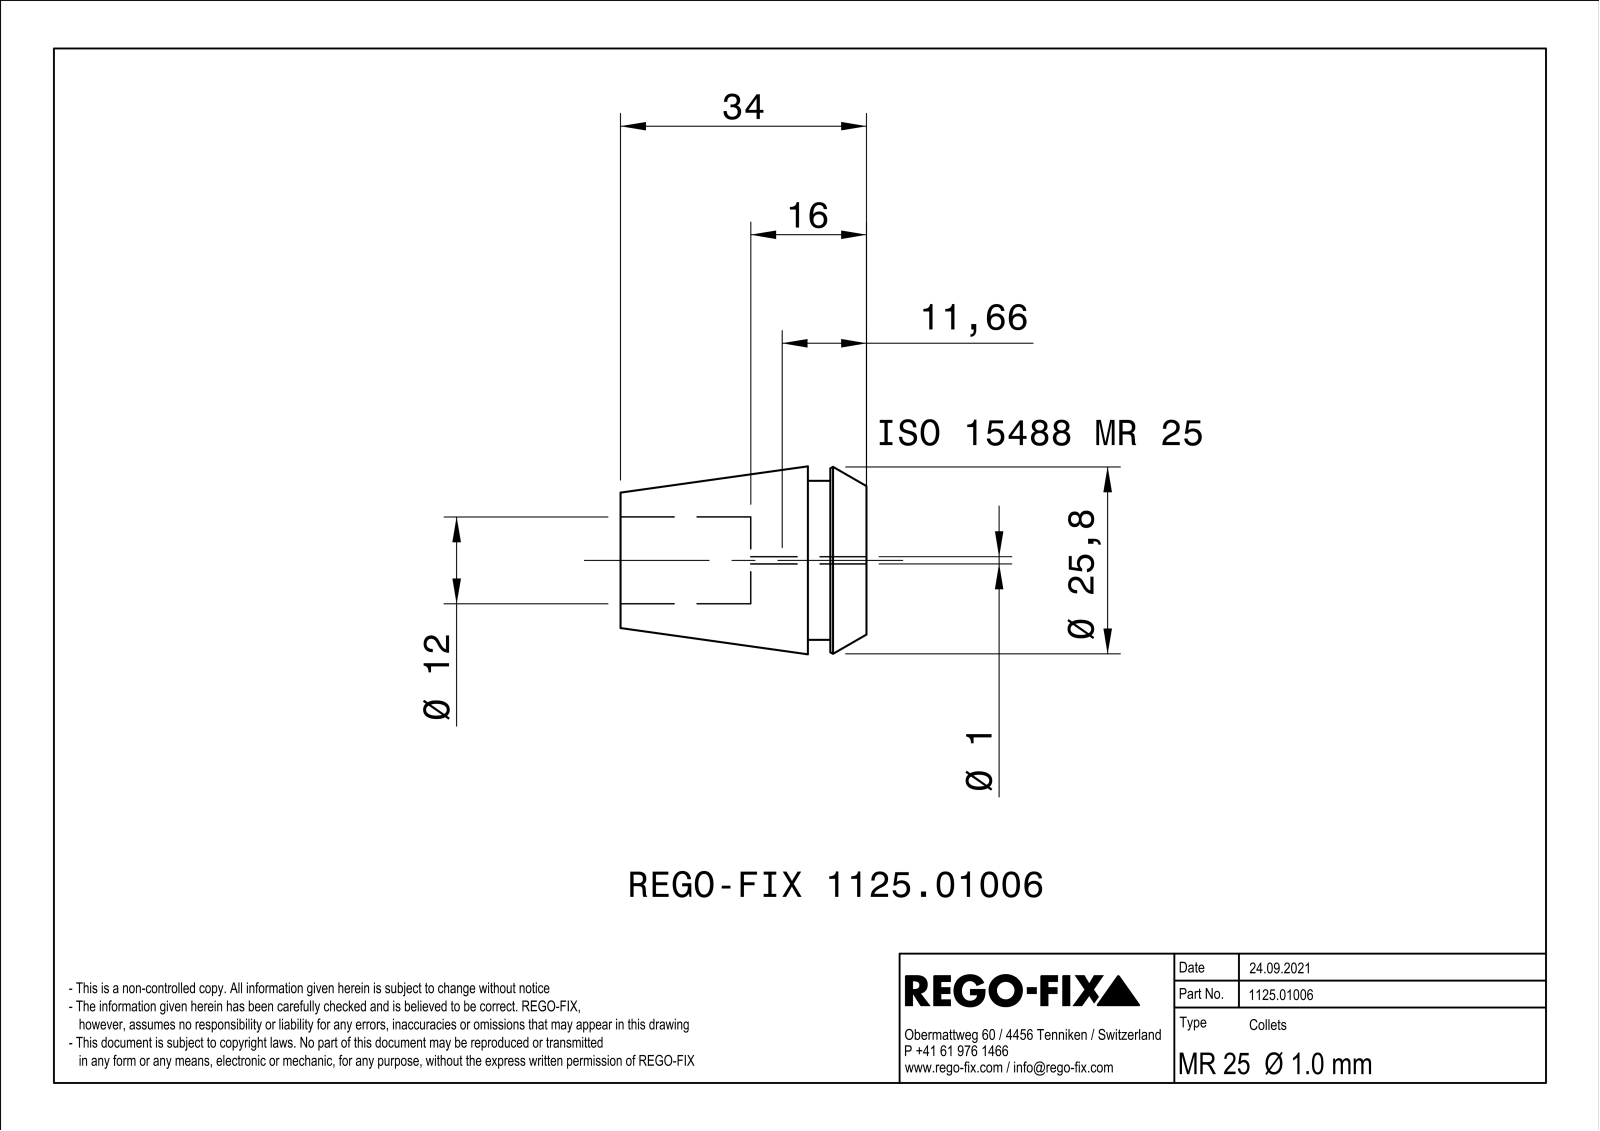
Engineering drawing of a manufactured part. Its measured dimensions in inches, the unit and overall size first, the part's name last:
Units: inches
Overall size (bounding box): 1.339 × 1.023 × 1.023
Round holes (diameter × count): ⌀0.472 ×1
Round bosses / shafts (diameter × count): ⌀0.866 ×1
Partial cylindrical surfaces — rounded edges, fillets, slot ends (radius × count): R0.016 ×14, R1.575 ×8, R0.02 ×1
Main face-to-face distances: 0.031, 0.032, 0.031, 0.025, 0.319, 1.339, 1.02, 0.197, 0.122, 1.142
Volume: 0.562 in³ · Surface area: 14.49 in²
Bodies: 1 solid, 268 faces (100 planar, 56 cylindrical, 112 other)
Part name (STEP PRODUCT): NOCUT
STEP written by: SIEMENS PLM Software Solid Edge ST10 (AUTOMOTIVE_DESIGN)
